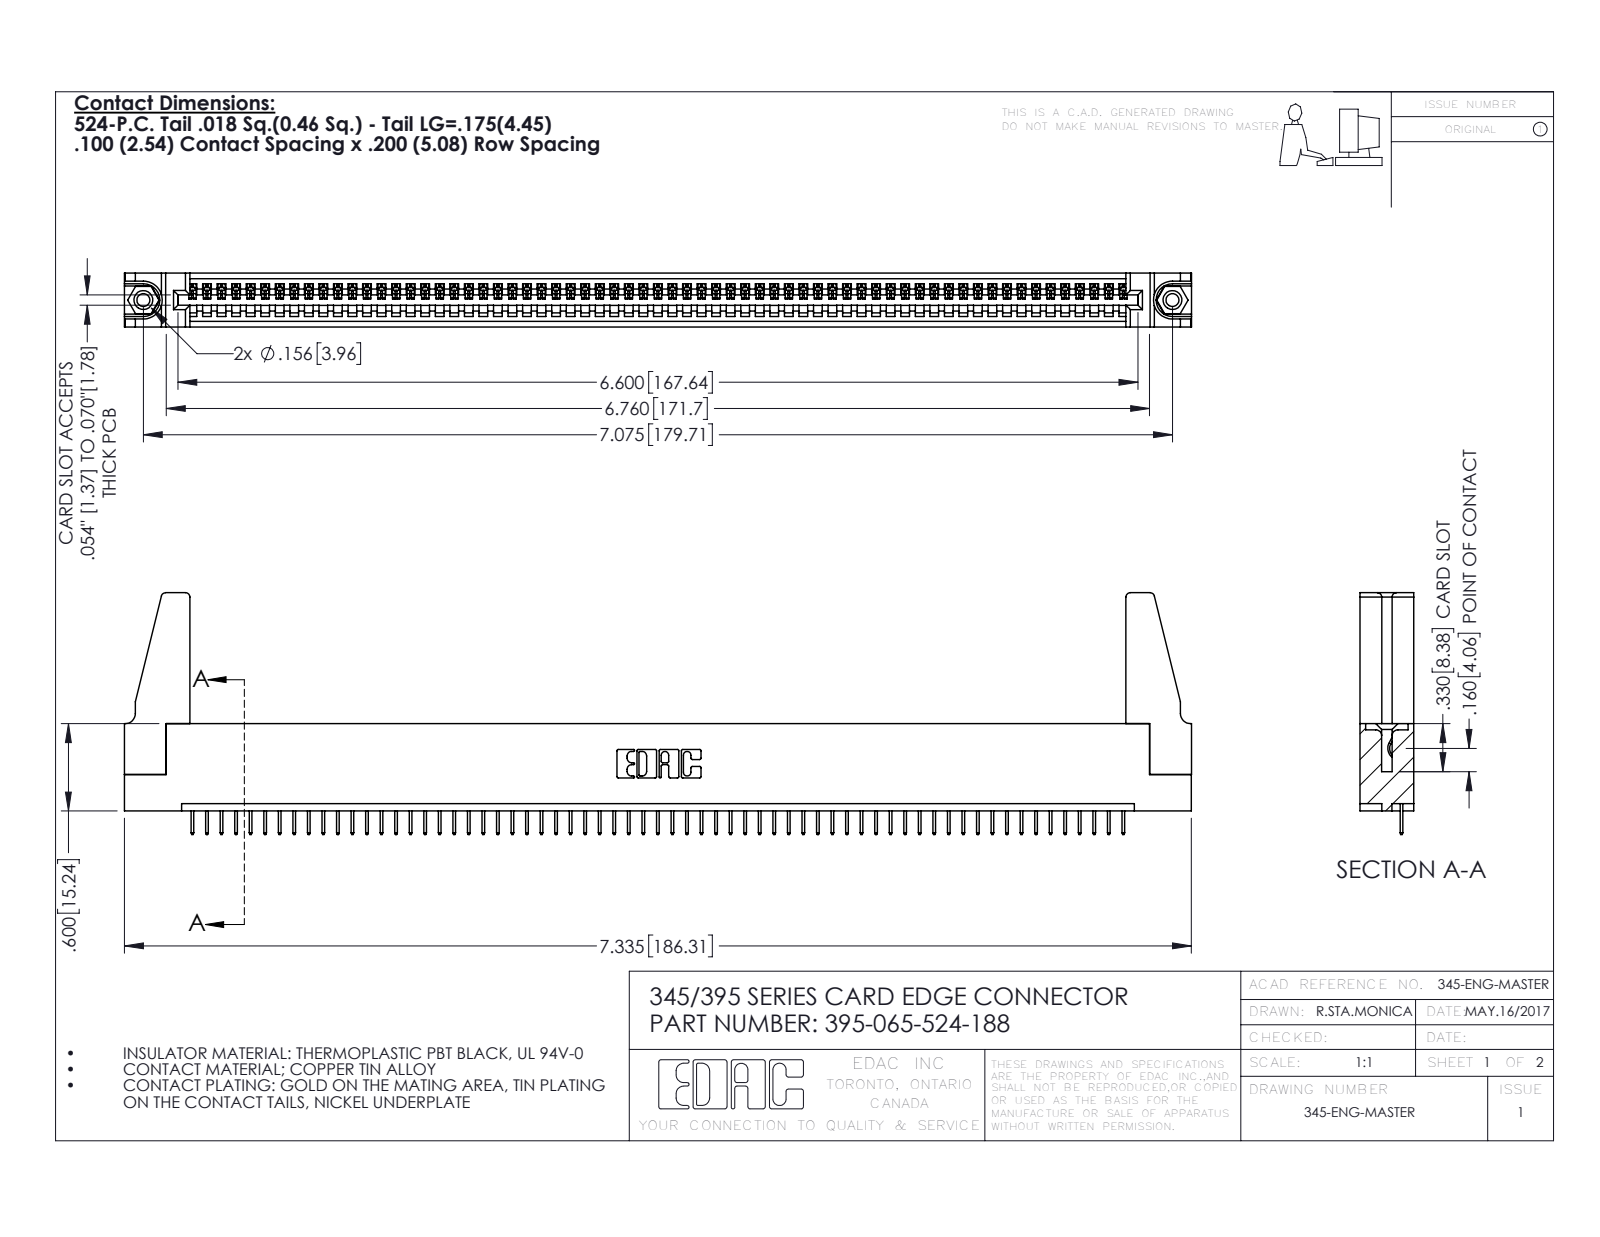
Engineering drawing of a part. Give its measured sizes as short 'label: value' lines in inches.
name: 395-065-524-188; 345-250-001_345-250-001-102; 345-292-001_345-293-124; 345-220-078_345-220-088 (+1 more)
written by: SolidWorks 2016 (CONFIG_CONTROL_DESIGN)
unit: in
bodies: 70 solids, 4280 faces (3142 planar, 1122 cylindrical, 16 other)
size: 7.336 × 1.662 × 0.37
volume: 1.274 in³; area: 40.38 in²
holes: 2× ⌀0.089, 2× ⌀0.125, 2× ⌀0.156, 1× ⌀0.064
bosses: 2× ⌀0.155
rounds: 130× R0.006, 22× R0.01, 8× R0.03, 6× R0.007, 6× R0.031, 3× R0.026, 2× R0.031, 2× R0.04
face distances: 0.072, 0.298, 0.37, 0.2, 0.098, 0.272, 0.025, 0.225, 0.072, 0.149
hole spacings: 0.27, 6.839, 7.075
